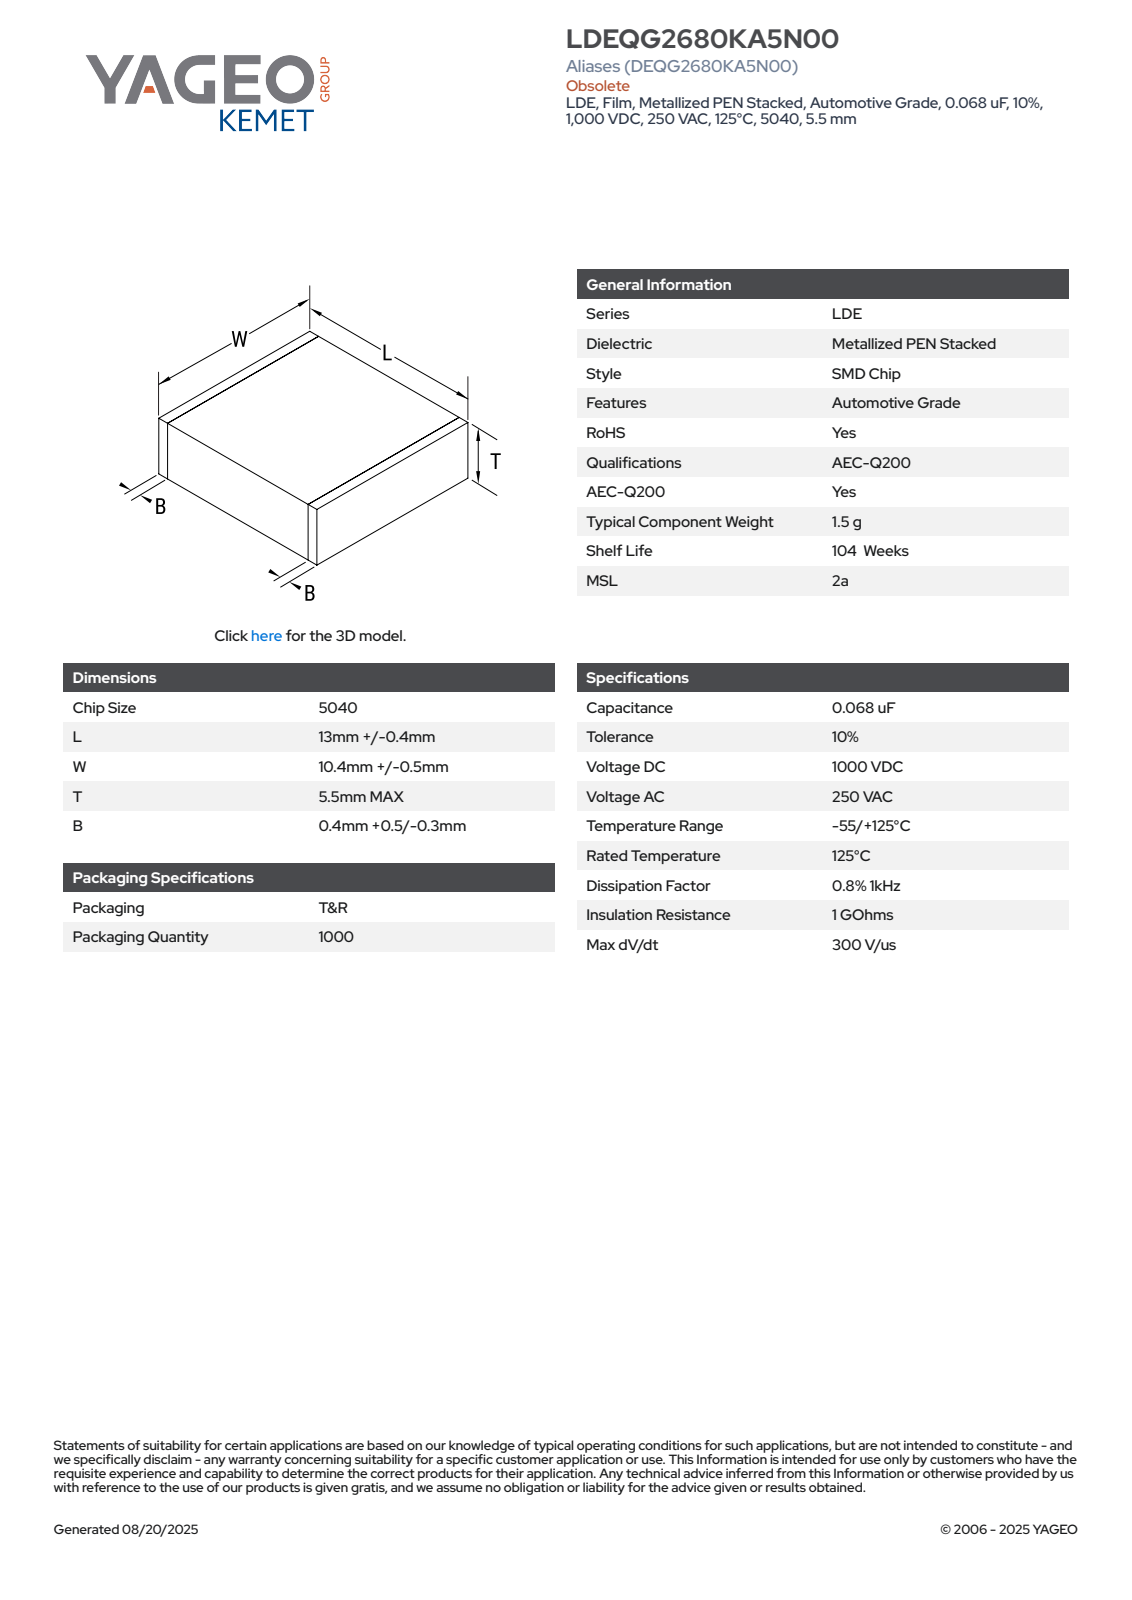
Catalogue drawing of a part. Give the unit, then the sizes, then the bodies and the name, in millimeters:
Units: millimetres
Overall size (bounding box): 13.4 × 10.9 × 5.5
Main face-to-face distances: 5.48, 10.88, 13.4, 5.49, 10.89, 5.5, 10.9, 0.5, 12.9, 12.4
Volume: 799 mm³ · Surface area: 568 mm²
Bodies: 4 solids, 73 faces (73 planar, 0 cylindrical, 0 other)
Part name (STEP PRODUCT): CFS_LDELDB_5040_L13.4W10.9T5.5B0.9
STEP written by: SolidWorks 2020 (AUTOMOTIVE_DESIGN)
